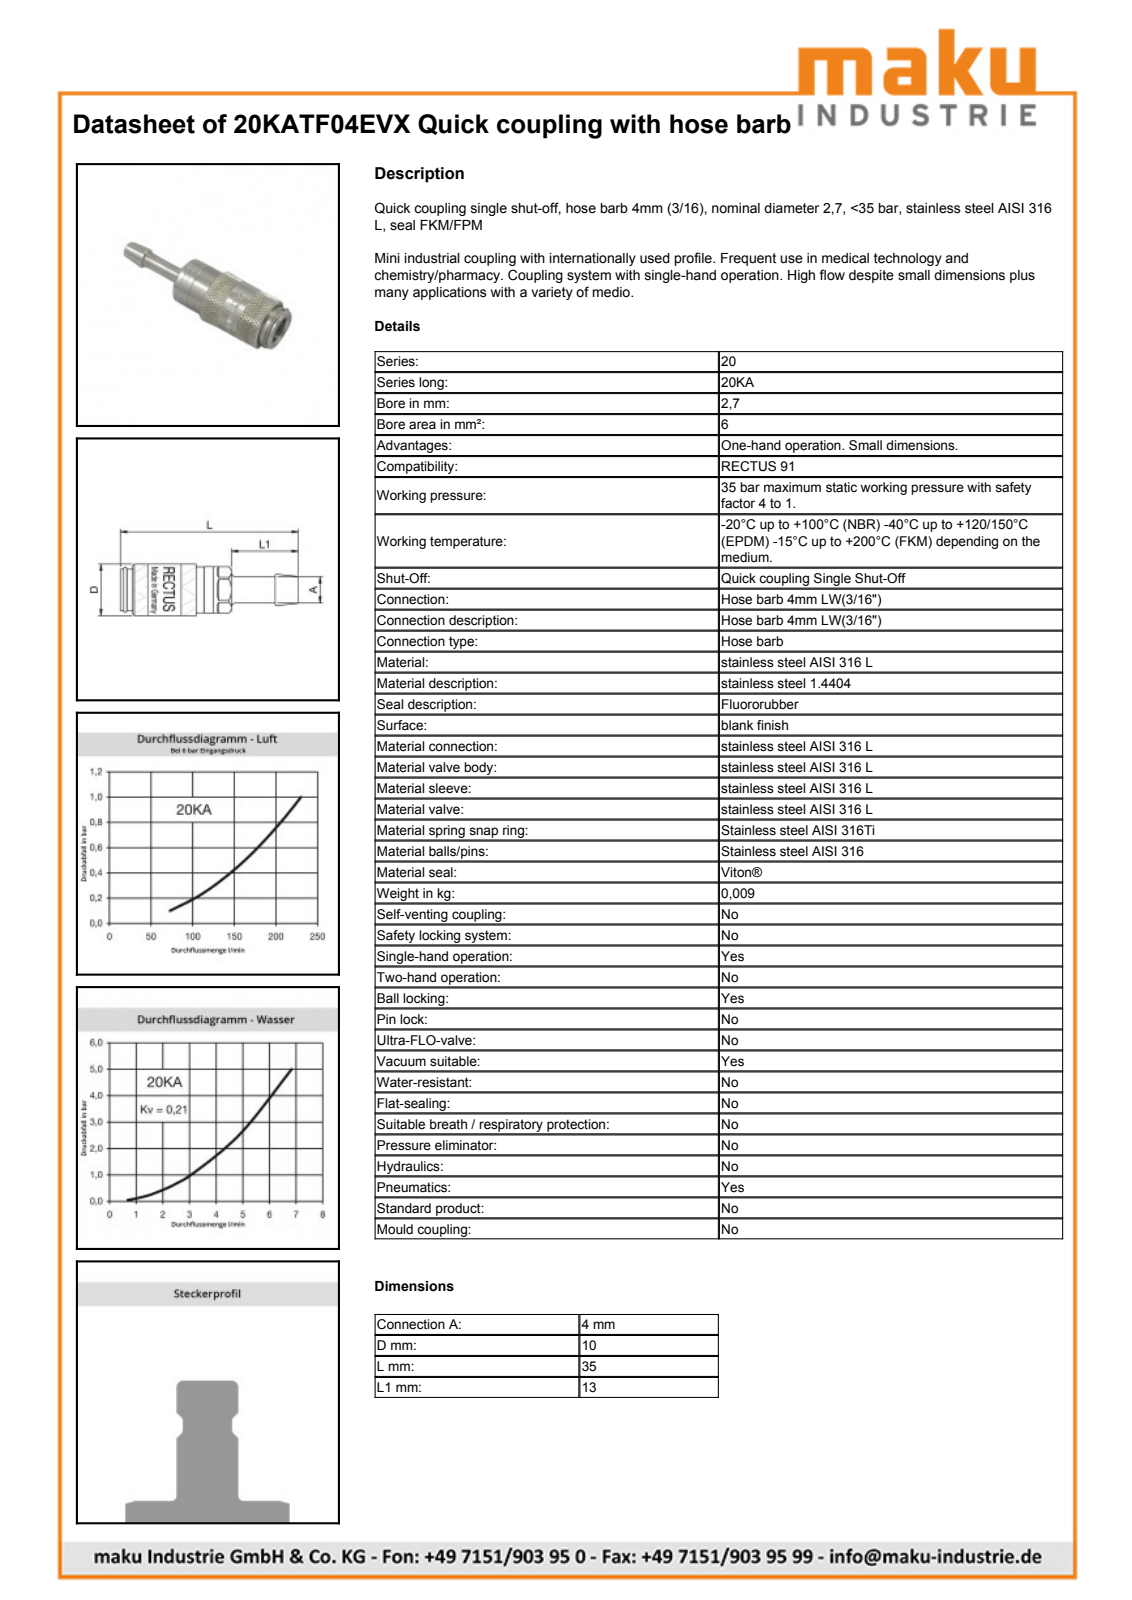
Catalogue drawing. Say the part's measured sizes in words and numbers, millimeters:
The part is named "D111895". Its 3-D file was written by "Autodesk Inventor 2013 (AUTOMOTIVE_DESIGN)". It is 2 solids with 449 faces: 164 planar, 55 cylindrical and 230 other. Overall it measures 34.55 by 10.35 by 10.35 millimeters. Its volume is 1 582 cubic millimeters and its surface area 1 906 square millimeters. Round holes: 1 of diameter 7.46, 1 of diameter 8.1, 1 of diameter 8.15, 1 of diameter 9.15, 1 of diameter 9.2. Round bosses or shafts: 1 of diameter 10.35, 1 of diameter 10, 1 of diameter 9, 1 of diameter 8.9, 1 of diameter 8, 1 of diameter 7.8, 1 of diameter 7.4, 1 of diameter 7.3. Partial cylindrical surfaces (rounded edges, fillets, slot ends): 1 of radius 4.9. The main face-to-face distances are 21.55, 8, 2.5, 19.05, 5, 3.2, 14.8, 12.3, 6.75, 13.
